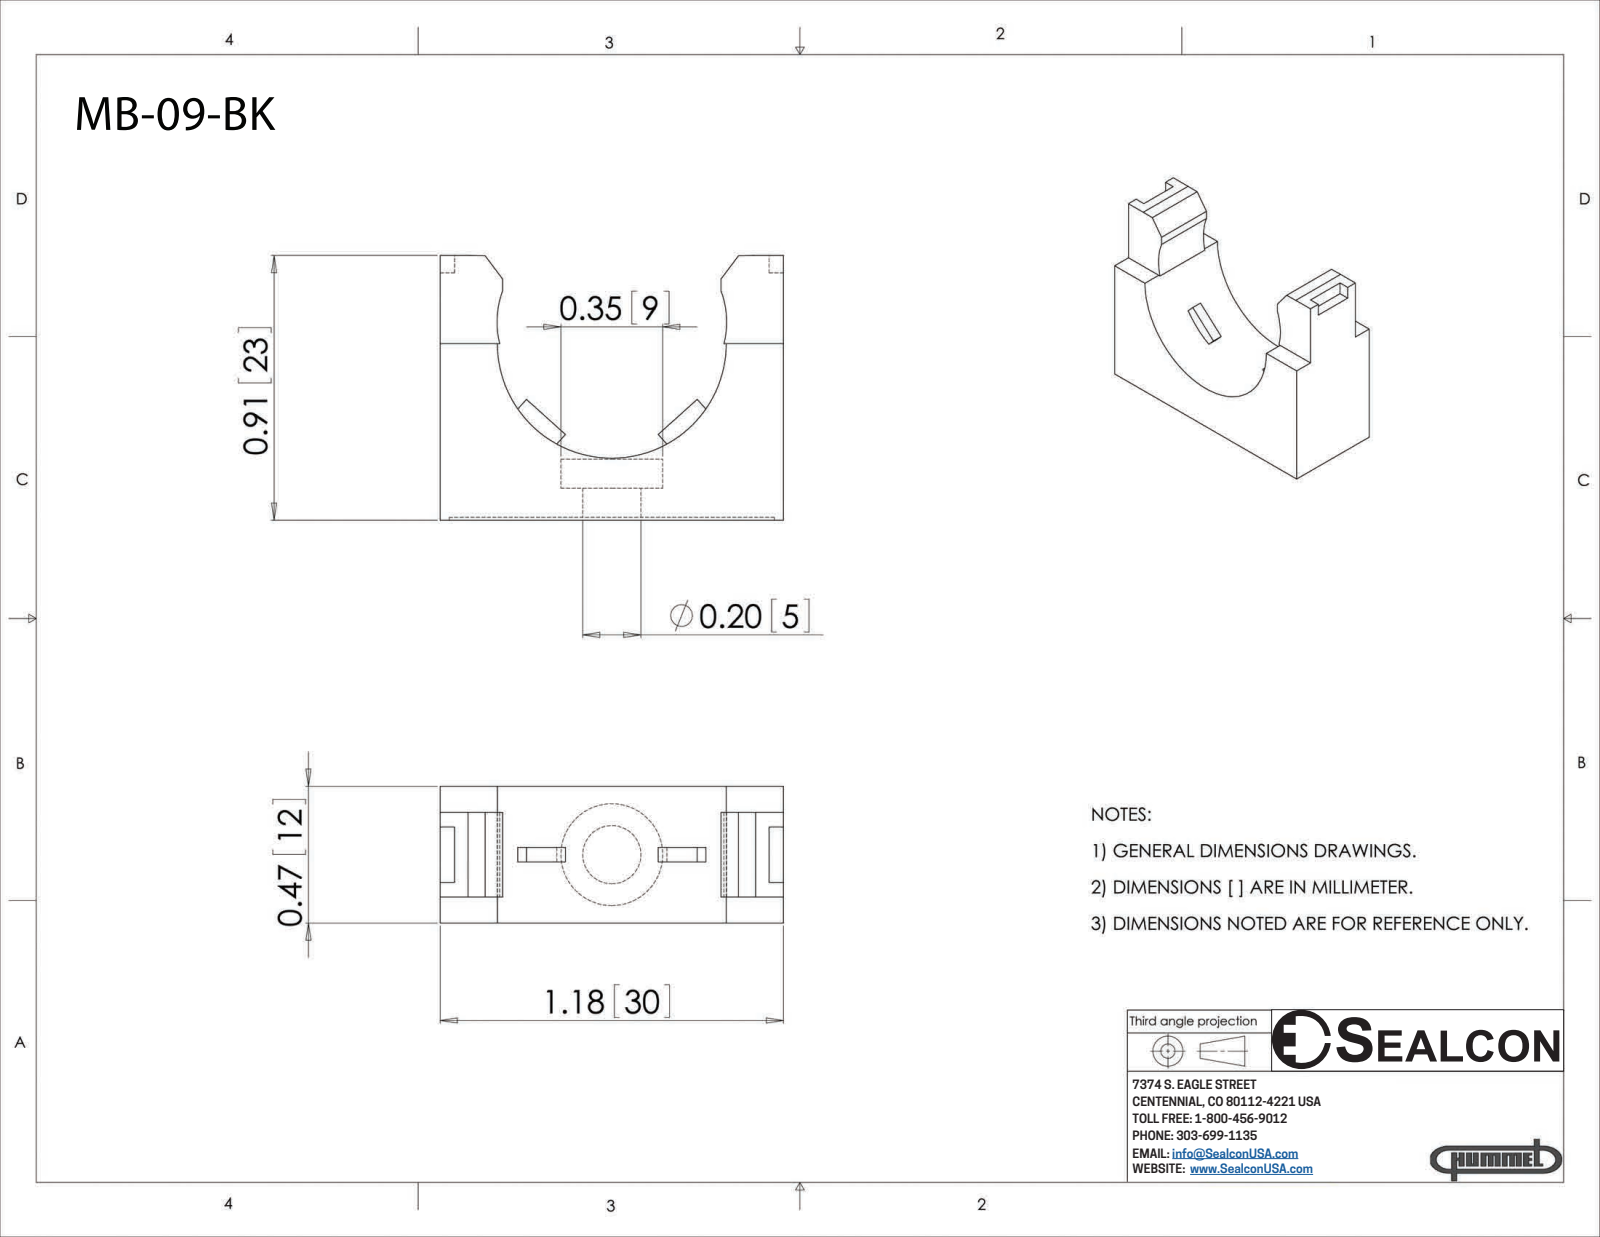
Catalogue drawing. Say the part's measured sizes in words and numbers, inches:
The part is named "MB-09-BK". Its 3-D file was written by "SolidWorks 2008 (CONFIG_CONTROL_DESIGN)". It is 1 solid with 56 faces: 48 planar, 8 cylindrical and 0 other. Overall it measures 1.18 by 0.91 by 0.47 inches. Its volume is 0.24 cubic inches and its surface area 3.813 square inches. Round holes: 1 of diameter 0.2, 1 of diameter 0.35. Partial cylindrical surfaces (rounded edges, fillets, slot ends): 2 of radius 0.31, 1 of radius 0.393. The main face-to-face distances are 0.47, 1.18, 0.1, 0.38, 0.09, 0.089, 0.291, 0.381, 0.21, 0.2.
